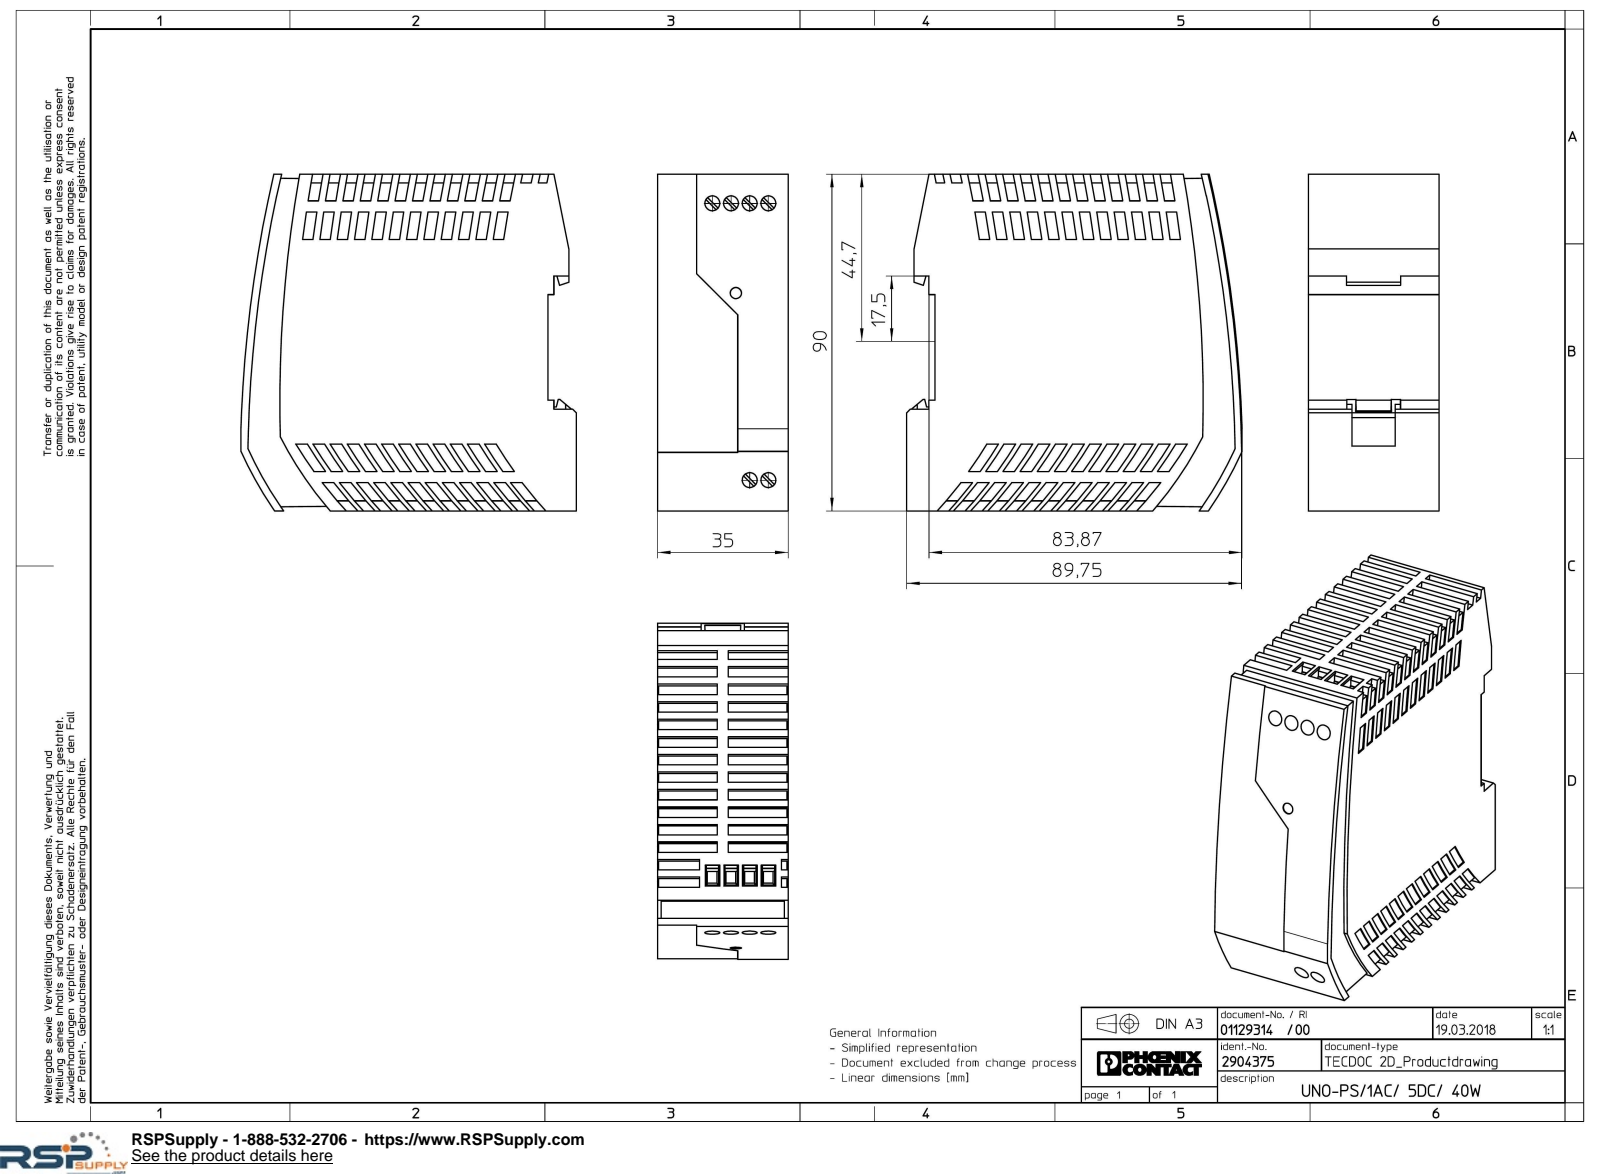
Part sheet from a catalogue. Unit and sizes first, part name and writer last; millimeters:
Units: millimetres
Overall size (bounding box): 90 × 89.87 × 35
Round holes (diameter × count): ⌀4 ×6
Partial cylindrical surfaces — rounded edges, fillets, slot ends (radius × count): R111 ×26, R98 ×1, R98.55 ×1, R100 ×1, R282.66 ×1, R284.9 ×1, R286.76 ×1, R291.36 ×1
Main face-to-face distances: 35, 34.7, 0.7, 1, 34, 33.7, 87.3, 2.7, 90, 87.7
Hole centre spacings: 5, 74.17, 10, 74, 74.67, 15, 75.5
Volume: 250 999 mm³ · Surface area: 33 871 mm²
Bodies: 1 solid, 779 faces (558 planar, 219 cylindrical, 2 other)
Part name (STEP PRODUCT): UNO_PS_1AC_5DC_40W-select
STEP written by: Creo Elements/Direct Modeling 18.1I 14-Aug-2016 (C) Parametric Technology GmbH (AUTOMOTIVE_DESIGN)
